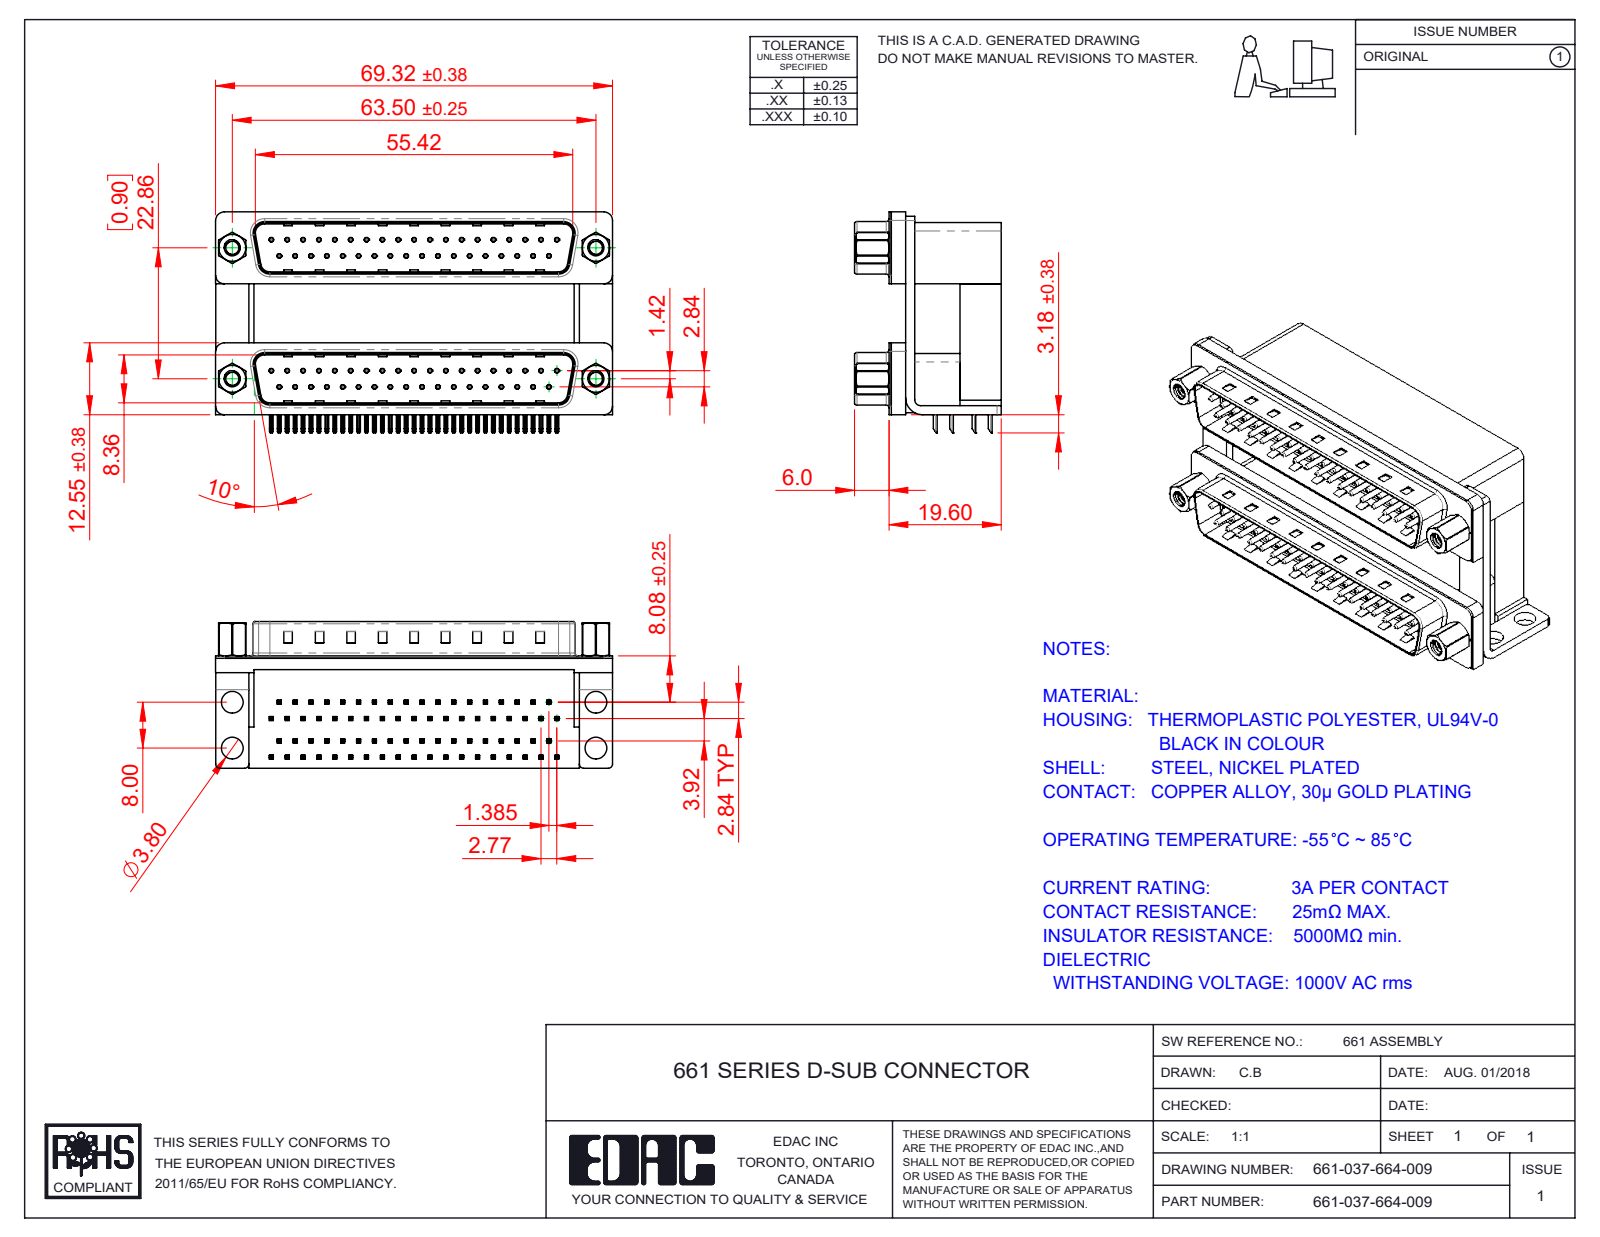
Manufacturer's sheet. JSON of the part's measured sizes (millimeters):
{"part_name": "661 Mounting Bracket_NoneH; 661 Contact Top Lower; 661-037-664-009; 661 Contact Top Upper_H (+8 more)", "step_written_by": "SolidWorks 2020 (CONFIG_CONTROL_DESIGN)", "units": "millimeters", "bodies": {"solids": 89, "faces": 6834, "planar": 4294, "cylindrical": 1938, "other": 602}, "overall_size": [69.32, 38.59, 25.6], "volume_mm3": 31233, "surface_area_mm2": 32115, "round_holes": [[0.35, 74], [0.8, 74], [2.26, 4], [2.29, 4], [3.5, 4], [3.8, 4], [4, 4], [4.8, 4], [5, 4]], "round_bosses_or_shafts": [[0.75, 74], [4.9, 4], [4.75, 4], [3.9, 4], [2.79, 4]], "partial_cylinders_radius": [[0.25, 296], [0.12, 148], [0.5, 16], [1.5, 14], [0.75, 8], [0.9, 8], [1.6, 8], [2, 8]], "face_to_face_distances": [12, 22.86, 19.2, 0.4, 7.2, 12.4, 10.7, 2.84, 8.76, 22.5], "hole_center_spacings": [2.77, 5.54, 3.16, 8.31, 11.08, 13.85, 16.62, 19.39]}
